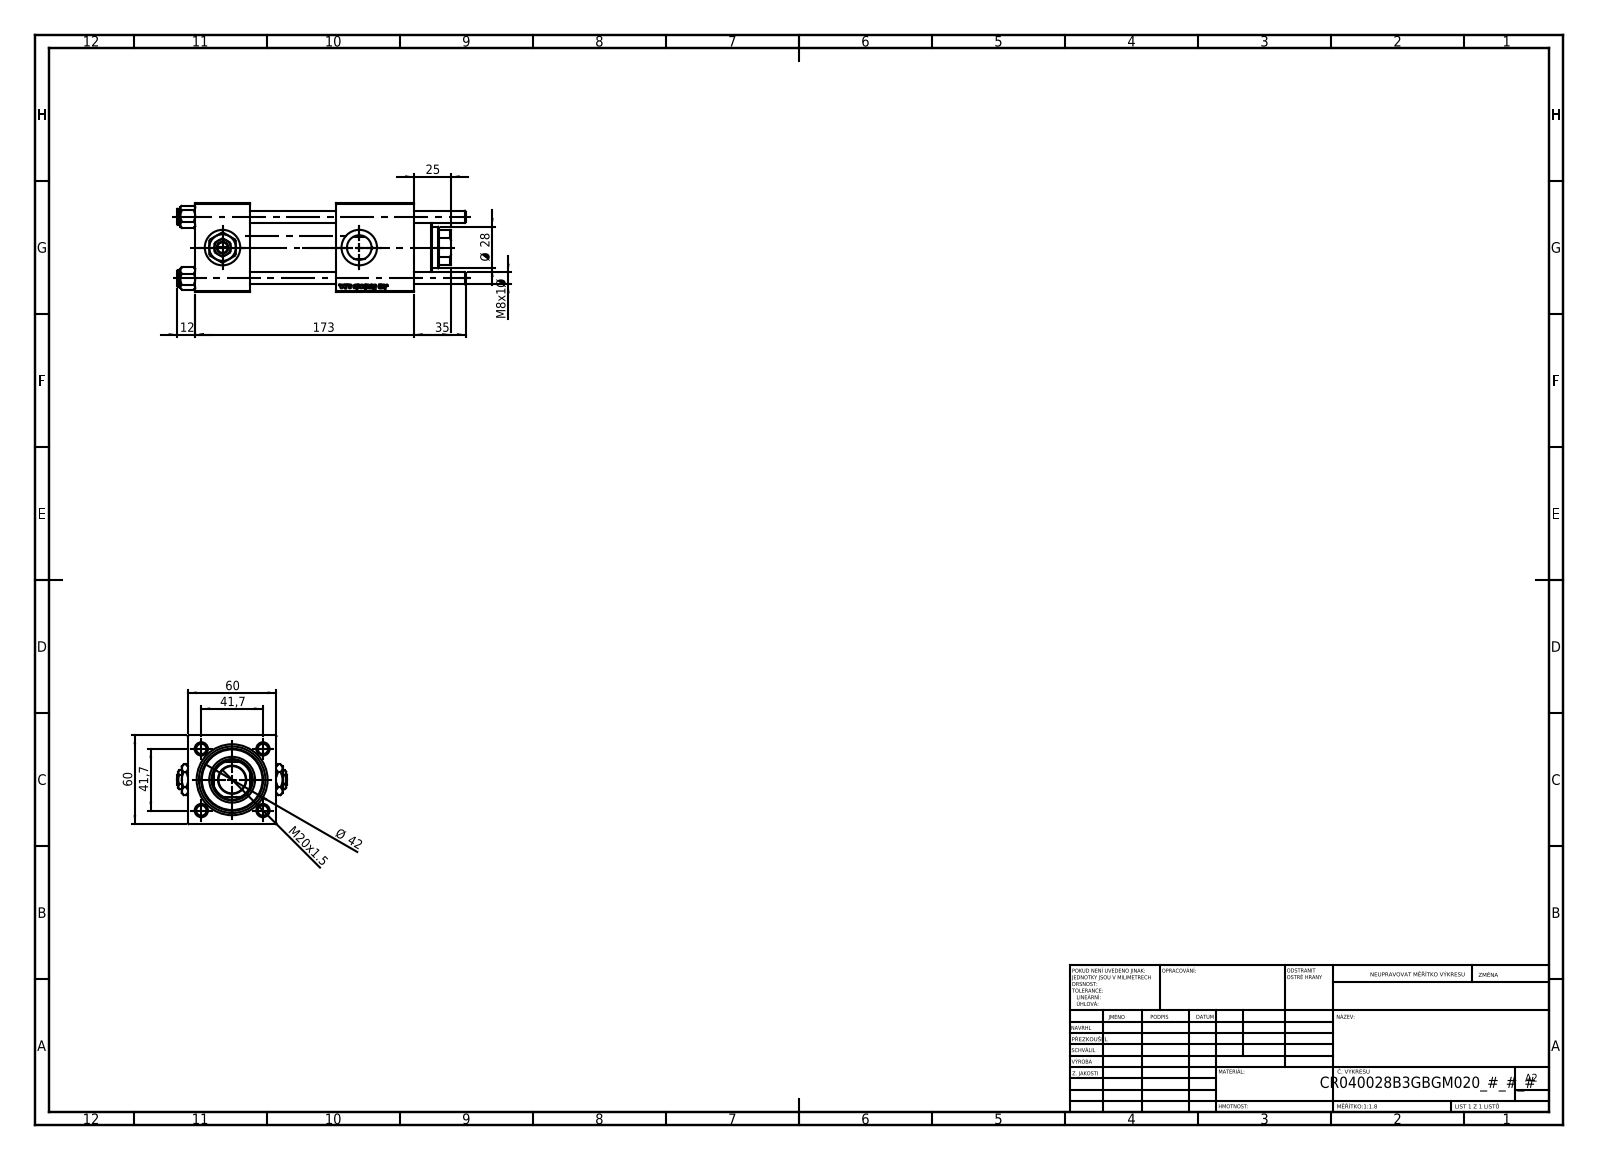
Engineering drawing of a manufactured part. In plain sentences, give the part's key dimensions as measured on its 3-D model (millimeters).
The part is named "V215CR_B-1; V215CR_VCP_B; NUT_M5_B; V215CR_B_TYCINKA (+2 more)". Its 3-D file was written by "SolidWorks 2019 (CONFIG_CONTROL_DESIGN)". It is 13 solids with 1259 faces: 481 planar, 88 cylindrical and 690 other. Overall it measures 195 by 74 by 60 millimeters. Its volume is 432 328 cubic millimeters and its surface area 122 775 square millimeters. Round holes: 4 of diameter 8, 2 of diameter 7, 2 of diameter 16.66, 2 of diameter 24, 1 of diameter 18.5, 1 of diameter 28, 1 of diameter 31, 1 of diameter 40, 1 of diameter 45. Round bosses or shafts: 4 of diameter 11, 1 of diameter 46, 1 of diameter 42. Partial cylindrical surfaces (rounded edges, fillets, slot ends): 1 of radius 13.5. The main face-to-face distances are 60, 37, 58, 95, 53, 119.3, 82.3, 24.3, 148, 111. The hole center spacings are 29.49, 41.7, 58.97, 92.5.
